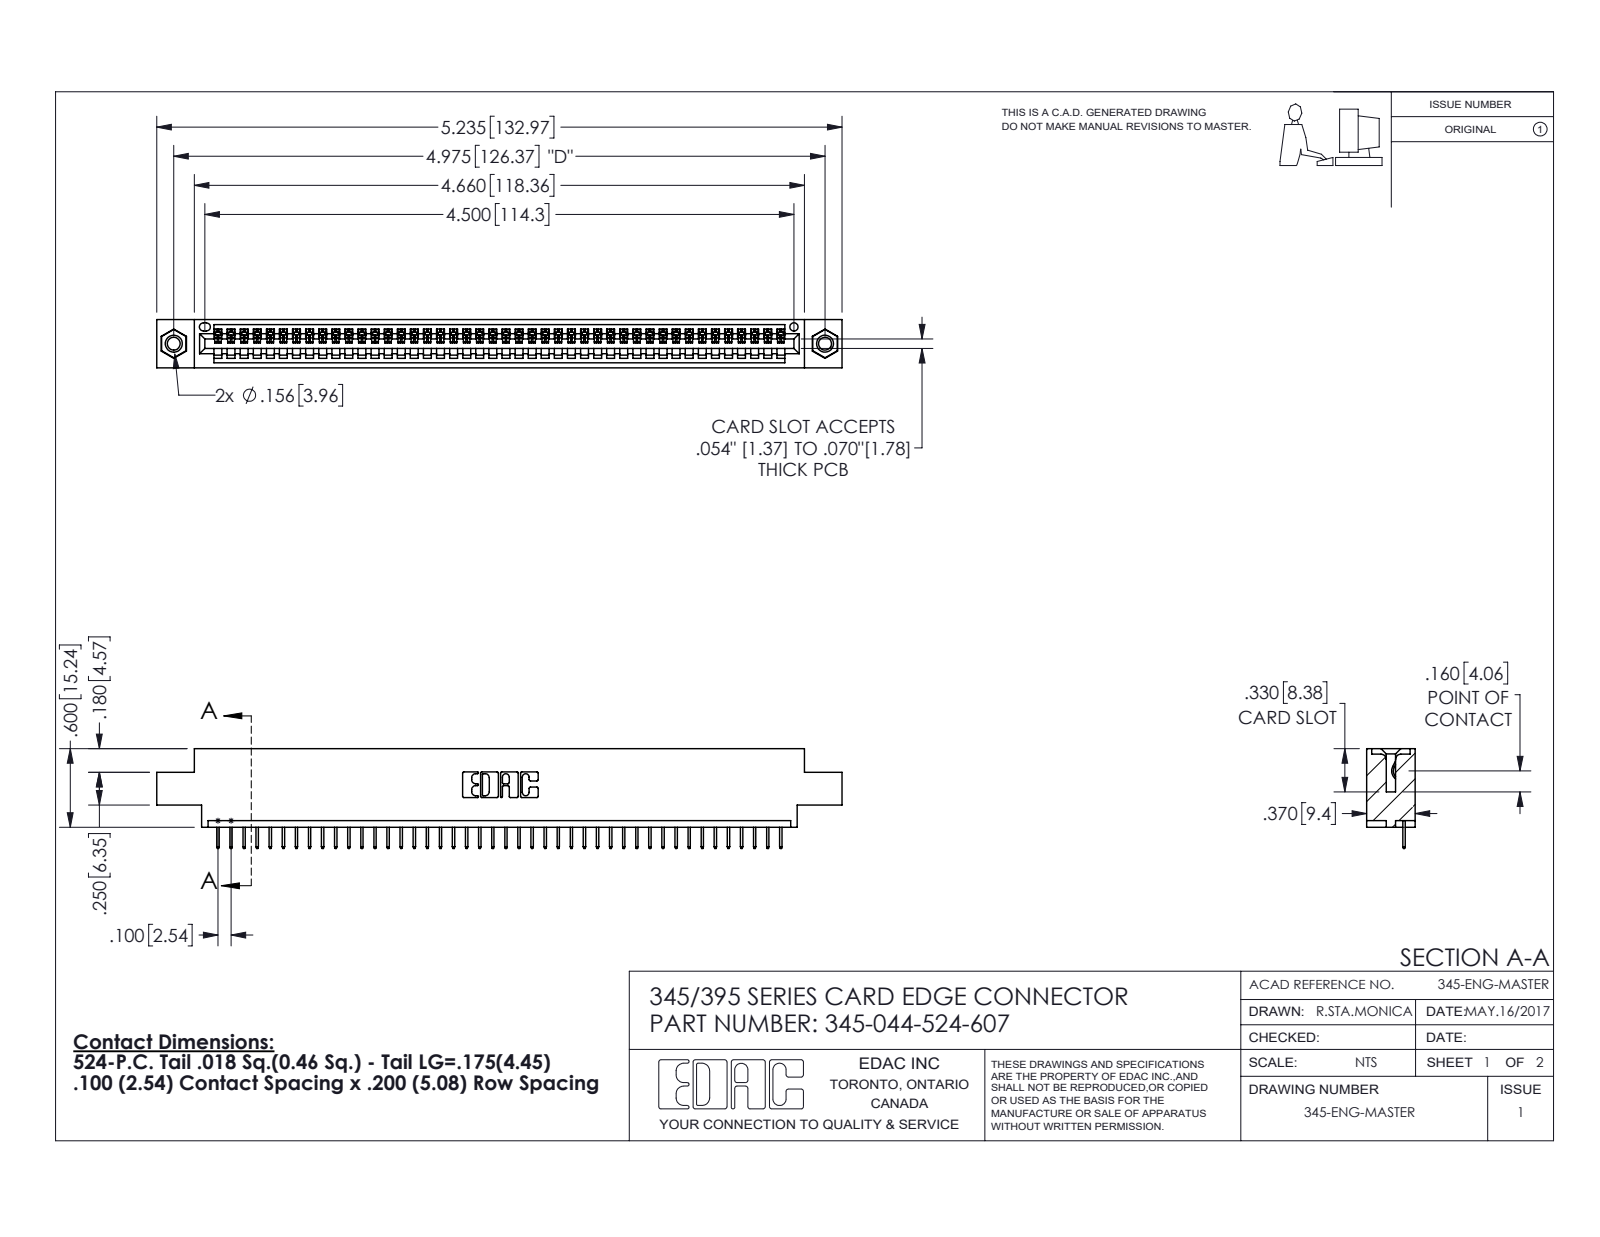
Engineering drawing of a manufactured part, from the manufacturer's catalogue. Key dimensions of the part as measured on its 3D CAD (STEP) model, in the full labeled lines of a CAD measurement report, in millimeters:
Part name (STEP PRODUCT): 345-250-001_345-250-005-103; 345-044-524-607; 345 Part_0.170 Offset - 0.156 Dia-TI; 345-292-001_345-293-124
STEP written by: SolidWorks 2016 (CONFIG_CONTROL_DESIGN)
Units: millimetres
Bodies: 47 solids, 2918 faces (2140 planar, 762 cylindrical, 16 other)
Overall size (bounding box): 133 × 19.4 × 9.4
Volume: 12 300 mm³ · Surface area: 16 040 mm²
Round holes (diameter × count): ⌀2.5 ×2, ⌀3.2 ×2, ⌀4 ×2, ⌀1.6 ×1
Round bosses / shafts (diameter × count): ⌀3.9 ×2
Partial cylindrical surfaces — rounded edges, fillets, slot ends (radius × count): R0.2 ×88, R0.3 ×22, R0.2 ×6, R0.8 ×6, R0.7 ×3, R0.8 ×2, R1 ×2, R0.4 ×1
Main face-to-face distances: 1.8, 7.6, 9.4, 5.1, 2.5, 6.9, 0.6, 5.7, 1.8, 4.4
Hole centre spacings: 6.9, 120.4, 126.4
